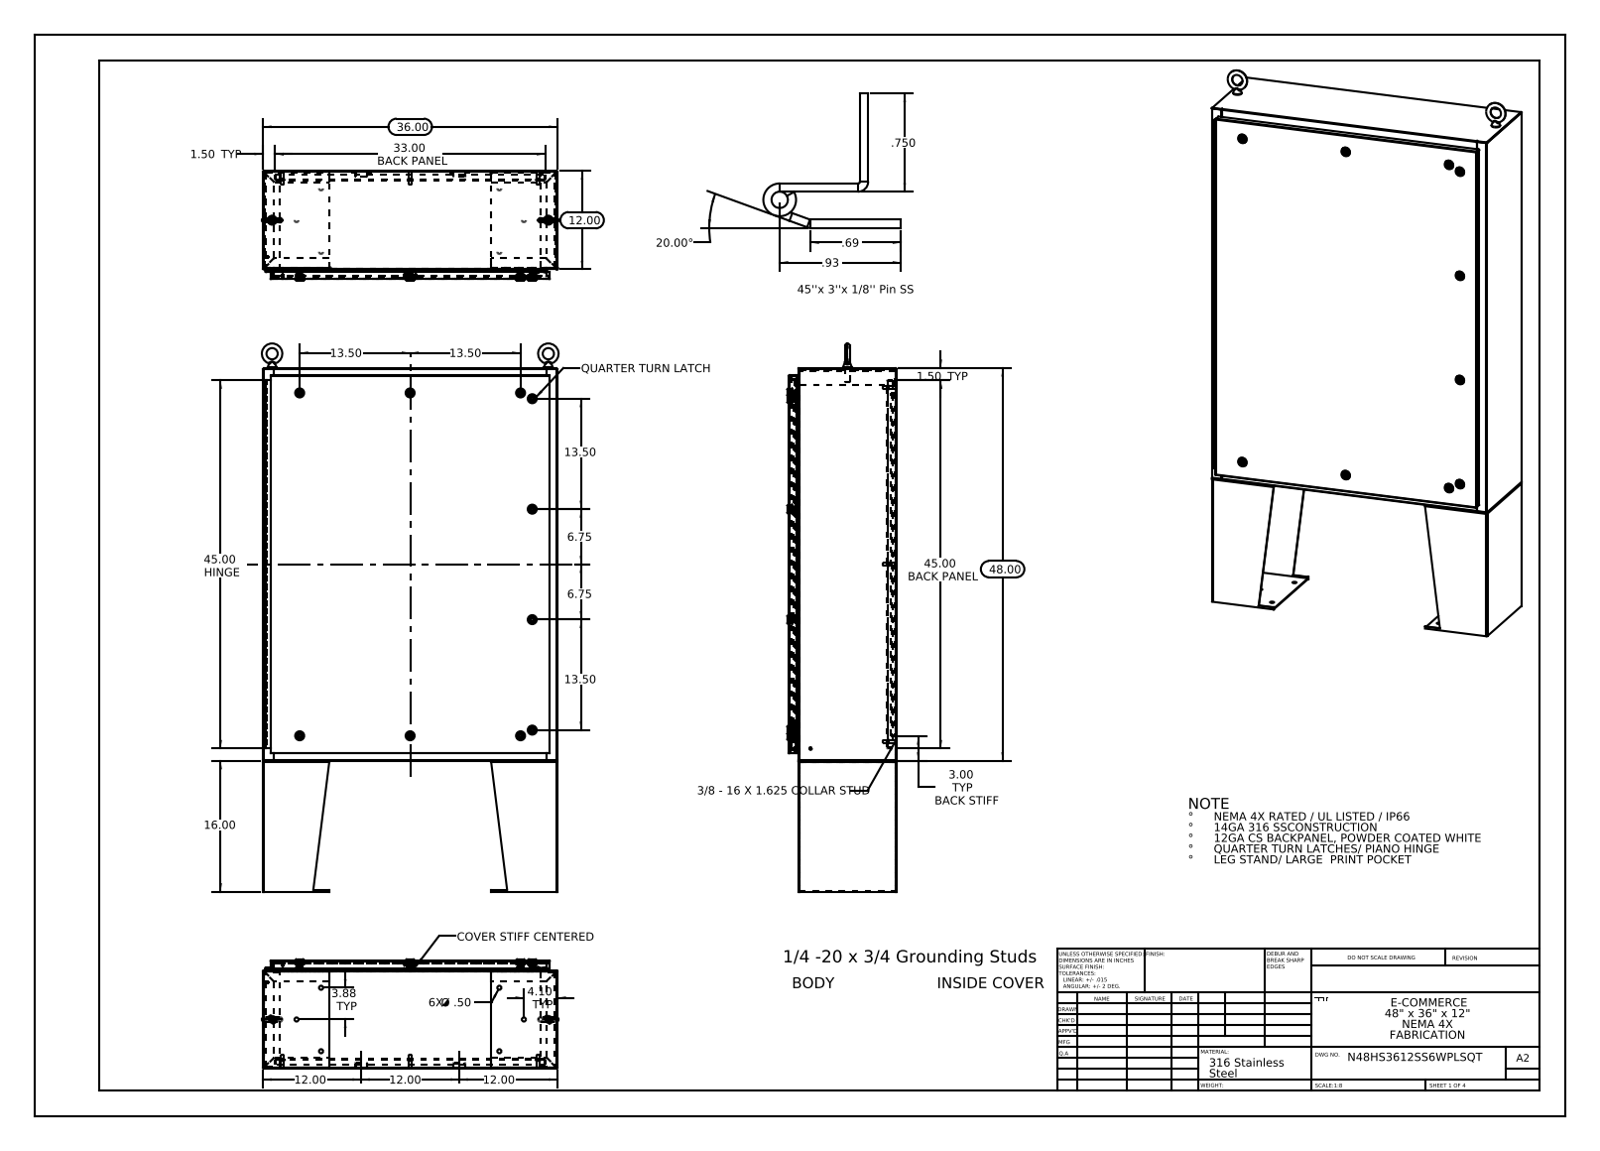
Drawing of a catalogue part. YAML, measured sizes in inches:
part_name: "N48HS3612SSWPLSQT SD-LSK - Base; Quarter-20 CD Stud; N48HS3612SSWPLSQT SD-LSK-Stand; 10_30 CD Stud (+8 more)"
step_written_by: "SolidWorks 2013 (CONFIG_CONTROL_DESIGN)"
units: inches
bodies: {solids: 34, faces: 2043, planar: 1041, cylindrical: 822, other: 180}
overall_size: [67, 36.271, 13.201]
volume: 769.9
surface_area: 18453
round_holes:
  - {diameter: 0.5, count: 14}
  - {diameter: 0.25, count: 6}
  - {diameter: 0.75, count: 4}
  - {diameter: 0.125, count: 1}
  - {diameter: 0.125, count: 1}
round_bosses_or_shafts:
  - {diameter: 0.625, count: 10}
  - {diameter: 0.375, count: 8}
  - {diameter: 0.33, count: 8}
  - {diameter: 0.157, count: 6}
  - {diameter: 0.14, count: 6}
  - {diameter: 0.315, count: 2}
  - {diameter: 0.236, count: 2}
  - {diameter: 0.25, count: 1}
partial_cylinders:
  - {radius: 0.013, count: 36}
  - {radius: 0.088, count: 30}
  - {radius: 0.442, count: 10}
  - {radius: 0.039, count: 8}
  - {radius: 0.143, count: 8}
  - {radius: 0.019, count: 6}
  - {radius: 0.117, count: 4}
  - {radius: 0.125, count: 4}
face_to_face_distances: [0.075, 13.126, 0.104, 13.051, 1.075, 13.201, 1, 12.126, 12.051, 1.179]
hole_center_spacings: [7.137, 20, 20.123, 21.625, 25.094, 38.003, 45.986, 2.225]
